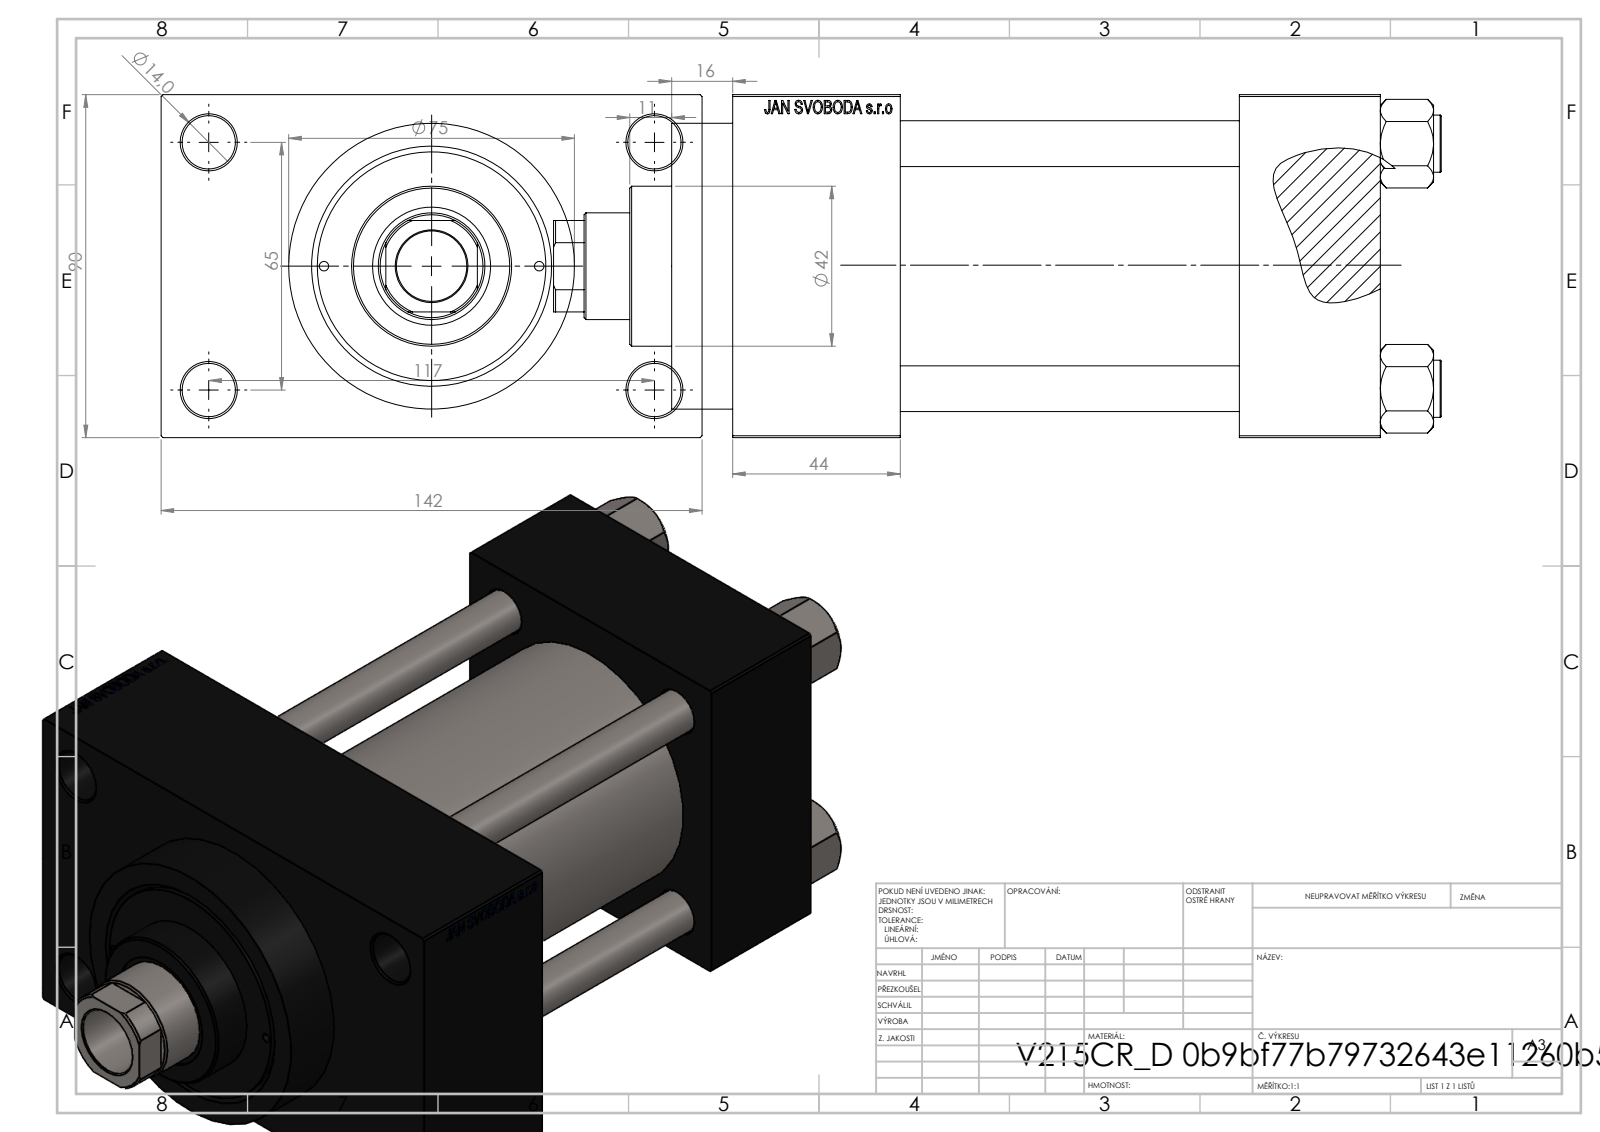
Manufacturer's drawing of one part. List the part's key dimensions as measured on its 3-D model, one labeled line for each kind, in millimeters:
Part name (STEP PRODUCT): V215CR_VCP_D; NUT_M5_D; V215CR_D_TYCINKA; V215CR_D_Body (+1 more)
STEP written by: SolidWorks 2019 (CONFIG_CONTROL_DESIGN)
Units: millimetres
Bodies: 11 solids, 1111 faces (499 planar, 92 cylindrical, 520 other)
Overall size (bounding box): 233 × 142 × 90
Volume: 1 147 000 mm³ · Surface area: 219 833 mm²
Round holes (diameter × count): ⌀12 ×4, ⌀14 ×4, ⌀2.5 ×2, ⌀7 ×2, ⌀20.96 ×2, ⌀30 ×2, ⌀18.5 ×1, ⌀28 ×1, ⌀31 ×1, ⌀50 ×1, ⌀60 ×1, ⌀63 ×1
Round bosses / shafts (diameter × count): ⌀15 ×4, ⌀75 ×1, ⌀69 ×1, ⌀42 ×1
Partial cylindrical surfaces — rounded edges, fillets, slot ends (radius × count): R13.5 ×1
Main face-to-face distances: 90, 89, 37, 126, 133, 170, 44, 26, 116, 142
Hole centre spacings: 26.35, 32.39, 44.4, 45.47, 64.3, 66.92, 68.42, 69.81
